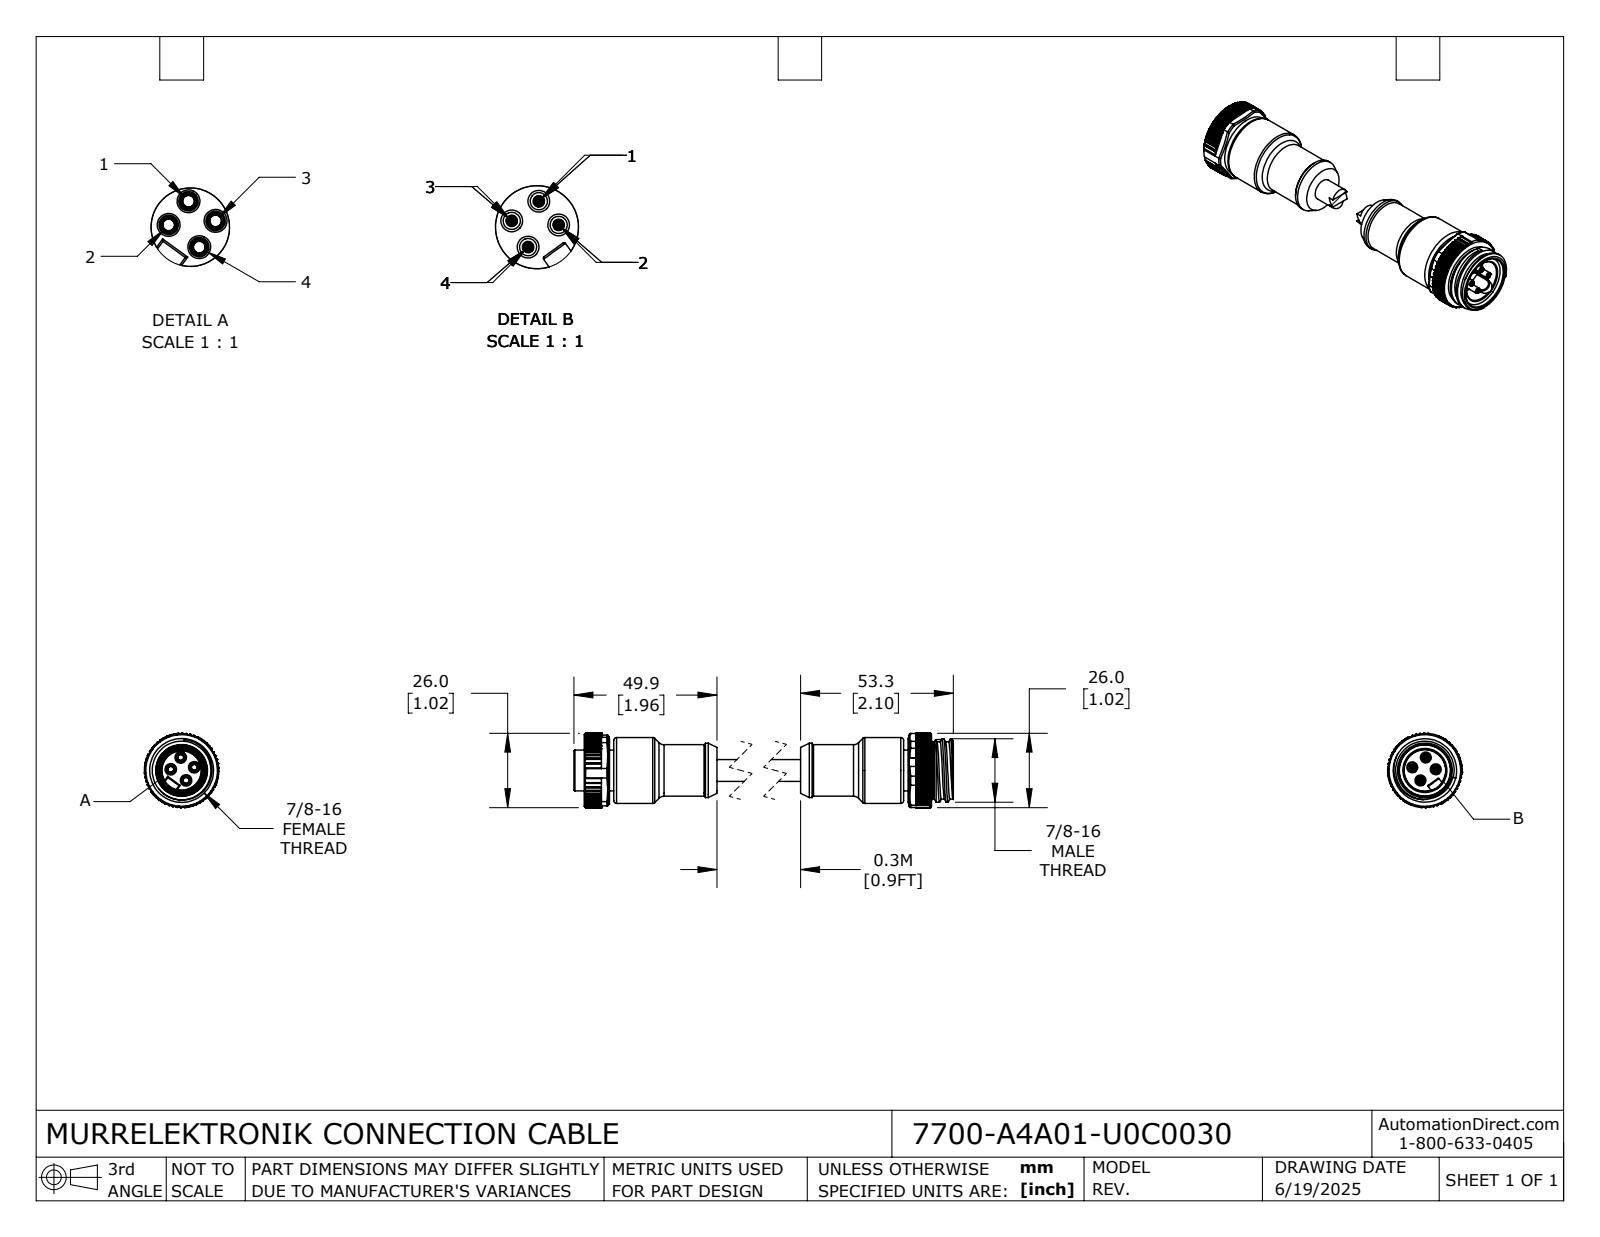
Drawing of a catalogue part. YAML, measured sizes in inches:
part_name: "7700-A4A01-U0C0030; 7700-A4A01-U0C0030_MALE; 7700-A4A01-U0C0030_FEMALE"
step_written_by: "SolidWorks 2024 (CONFIG_CONTROL_DESIGN)"
units: inches
bodies: {solids: 2, faces: 1226, planar: 520, cylindrical: 543, other: 163}
overall_size: [5.244, 1.024, 1.024]
volume: 2.059
surface_area: 22.09
round_holes:
  - {diameter: 0.081, count: 4}
  - {diameter: 0.118, count: 4}
  - {diameter: 0.134, count: 4}
  - {diameter: 0.61, count: 1}
  - {diameter: 0.614, count: 1}
  - {diameter: 0.728, count: 1}
  - {diameter: 0.807, count: 1}
  - {diameter: 0.875, count: 1}
round_bosses_or_shafts:
  - {diameter: 0.079, count: 4}
  - {diameter: 0.906, count: 1}
  - {diameter: 0.873, count: 1}
  - {diameter: 0.789, count: 1}
  - {diameter: 0.787, count: 1}
  - {diameter: 0.748, count: 1}
  - {diameter: 0.713, count: 1}
  - {diameter: 0.709, count: 1}
partial_cylinders:
  - {radius: 0.008, count: 252}
  - {radius: 0.012, count: 18}
  - {radius: 0.004, count: 8}
  - {radius: 0.027, count: 4}
  - {radius: 0.029, count: 4}
  - {radius: 0.093, count: 1}
  - {radius: 0.512, count: 1}
face_to_face_distances: [0.059, 4.075, 1.476, 2.657, 1.417, 2.598, 4.134, 0.346, 4.421, 0.287]
hole_center_spacings: [0.15, 0.324, 0.179, 0.179, 0.212, 0.213, 0.23, 0.26]
